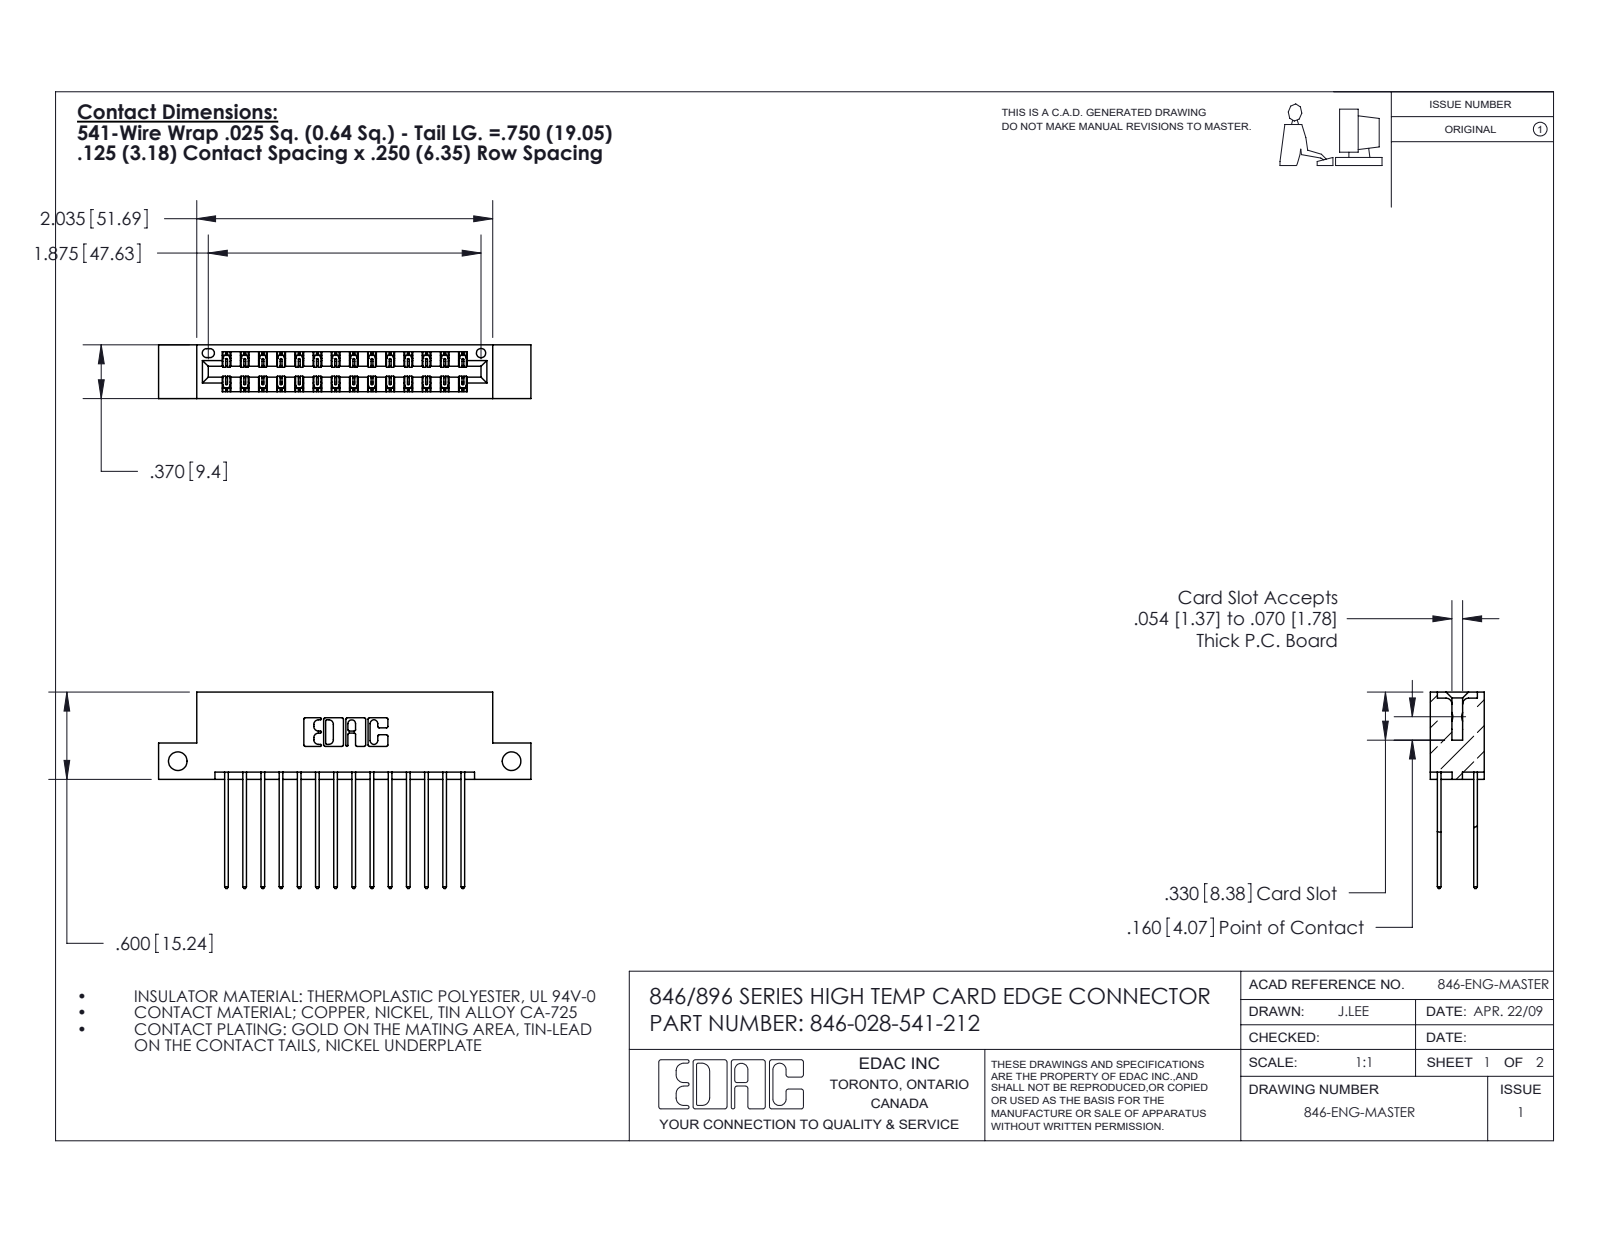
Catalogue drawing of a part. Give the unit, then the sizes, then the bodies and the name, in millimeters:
Units: millimetres
Overall size (bounding box): 65 × 34.3 × 9.4
Round holes (diameter × count): ⌀3.3 ×2, ⌀1.6 ×1
Partial cylindrical surfaces — rounded edges, fillets, slot ends (radius × count): R0.2 ×42, R0.3 ×28, R0.3 ×22, R0.2 ×6, R0.8 ×6, R0.7 ×3, R0.4 ×2, R0.6 ×2
Main face-to-face distances: 6.4, 1.2, 8.2, 1.8, 7.6, 0.6, 9.4, 7, 3.8, 5.6
Hole centre spacings: 58.3
Volume: 6 190 mm³ · Surface area: 8 710 mm²
Bodies: 29 solids, 1578 faces (1056 planar, 522 cylindrical, 0 other)
Part name (STEP PRODUCT): 346 Part_Flush Mounting Lugs - Side Mount; 345-292-001_345-293-141; 346-028-541-212
STEP written by: SolidWorks 2016 (CONFIG_CONTROL_DESIGN)
